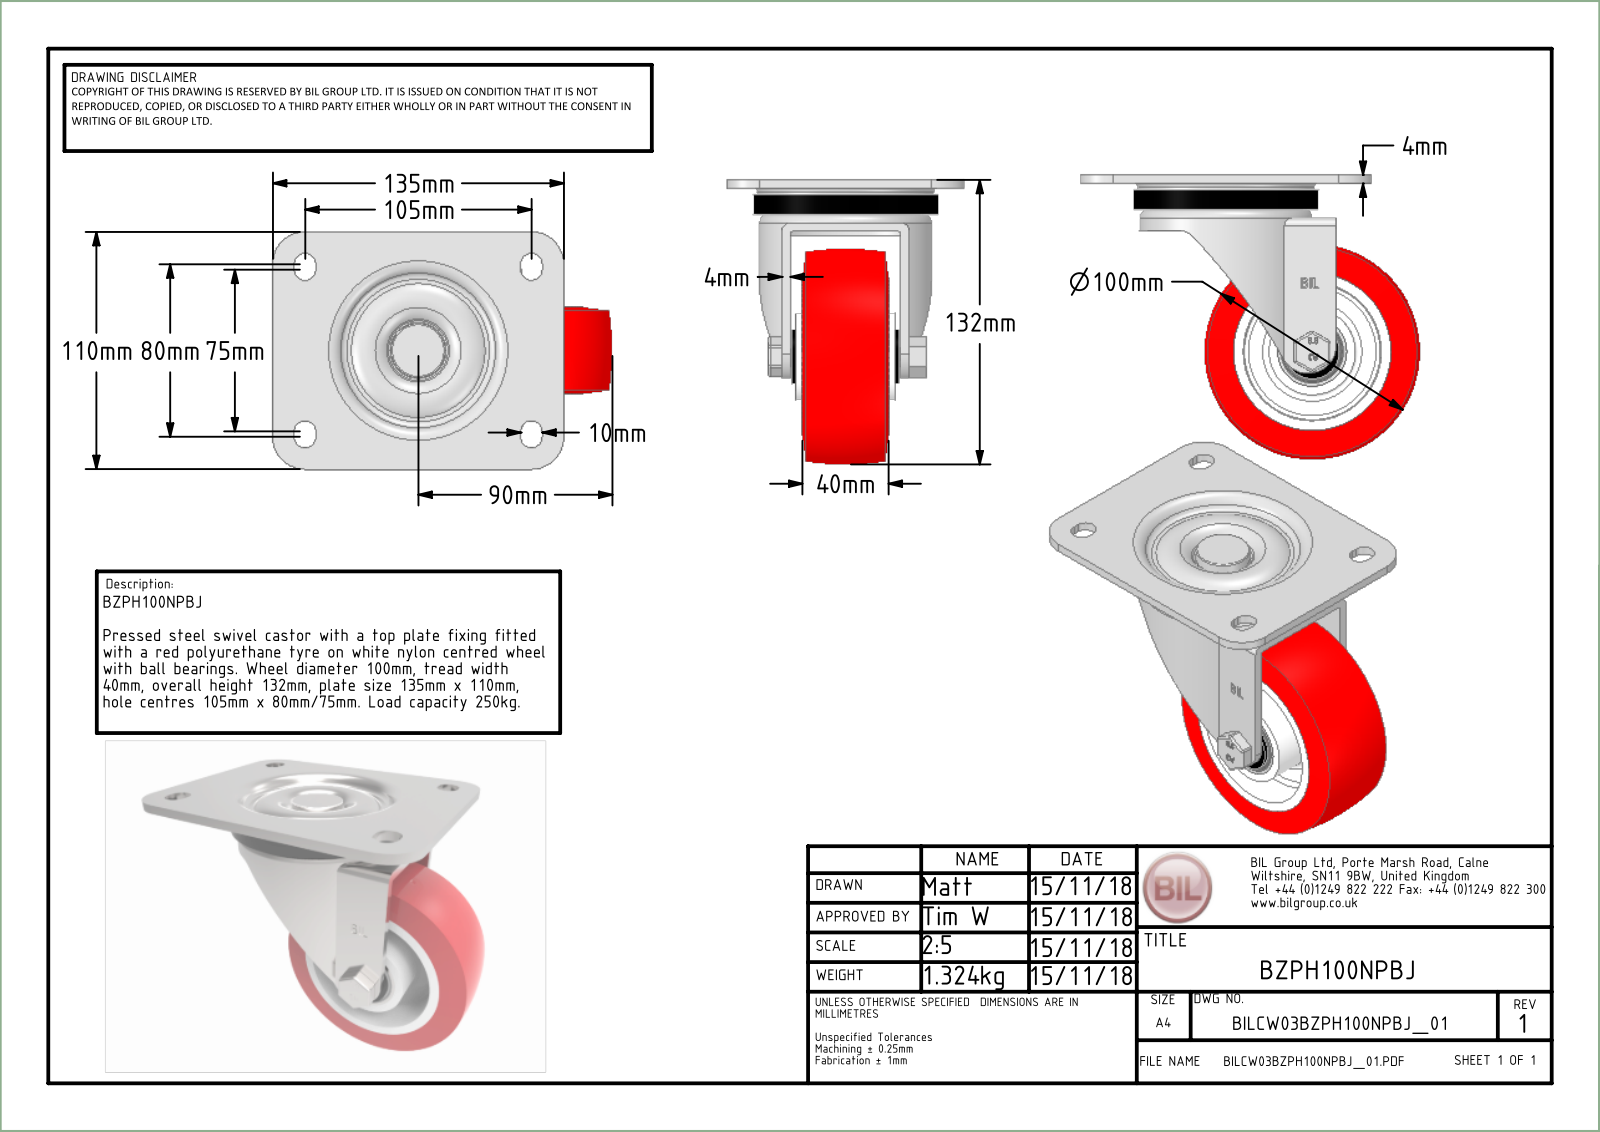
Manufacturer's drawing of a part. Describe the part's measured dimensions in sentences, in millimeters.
The part is named "BZPH100NPBJ v3; BZPH100AS - 52 v1; BZPH100AS v1; ZINC PLATED, PRESSED STEEL TOP PLATE (+8 more)". Its 3-D file was written by "Autodesk Translation Framework v14.10.0.0 (AUTOMOTIVE_DESIGN)". It is 41 solids with 1156 faces: 435 planar, 195 cylindrical and 526 other. Overall it measures 157.5 by 132 by 110 millimeters. Its volume is 389 873 cubic millimeters and its surface area 163 349 square millimeters. Round holes: 2 of diameter 28, 1 of diameter 10, 1 of diameter 10.2, 1 of diameter 10.5, 1 of diameter 12, 1 of diameter 15, 1 of diameter 15.75, 1 of diameter 20.5, 1 of diameter 26, 1 of diameter 26.8, 1 of diameter 28.2, 1 of diameter 30. Round bosses or shafts: 2 of diameter 25, 1 of diameter 83.5, 1 of diameter 80, 1 of diameter 51, 1 of diameter 40, 1 of diameter 32, 1 of diameter 21.5, 1 of diameter 21. Partial cylindrical surfaces (rounded edges, fillets, slot ends): 18 of radius 0.5, 8 of radius 5.5, 6 of radius 0.75, 4 of radius 2, 4 of radius 15, 2 of radius 4, 1 of radius 11.4, 1 of radius 12.9. The main face-to-face distances are 4, 9, 13, 6, 50, 40, 10, 5, 46, 17.5.
